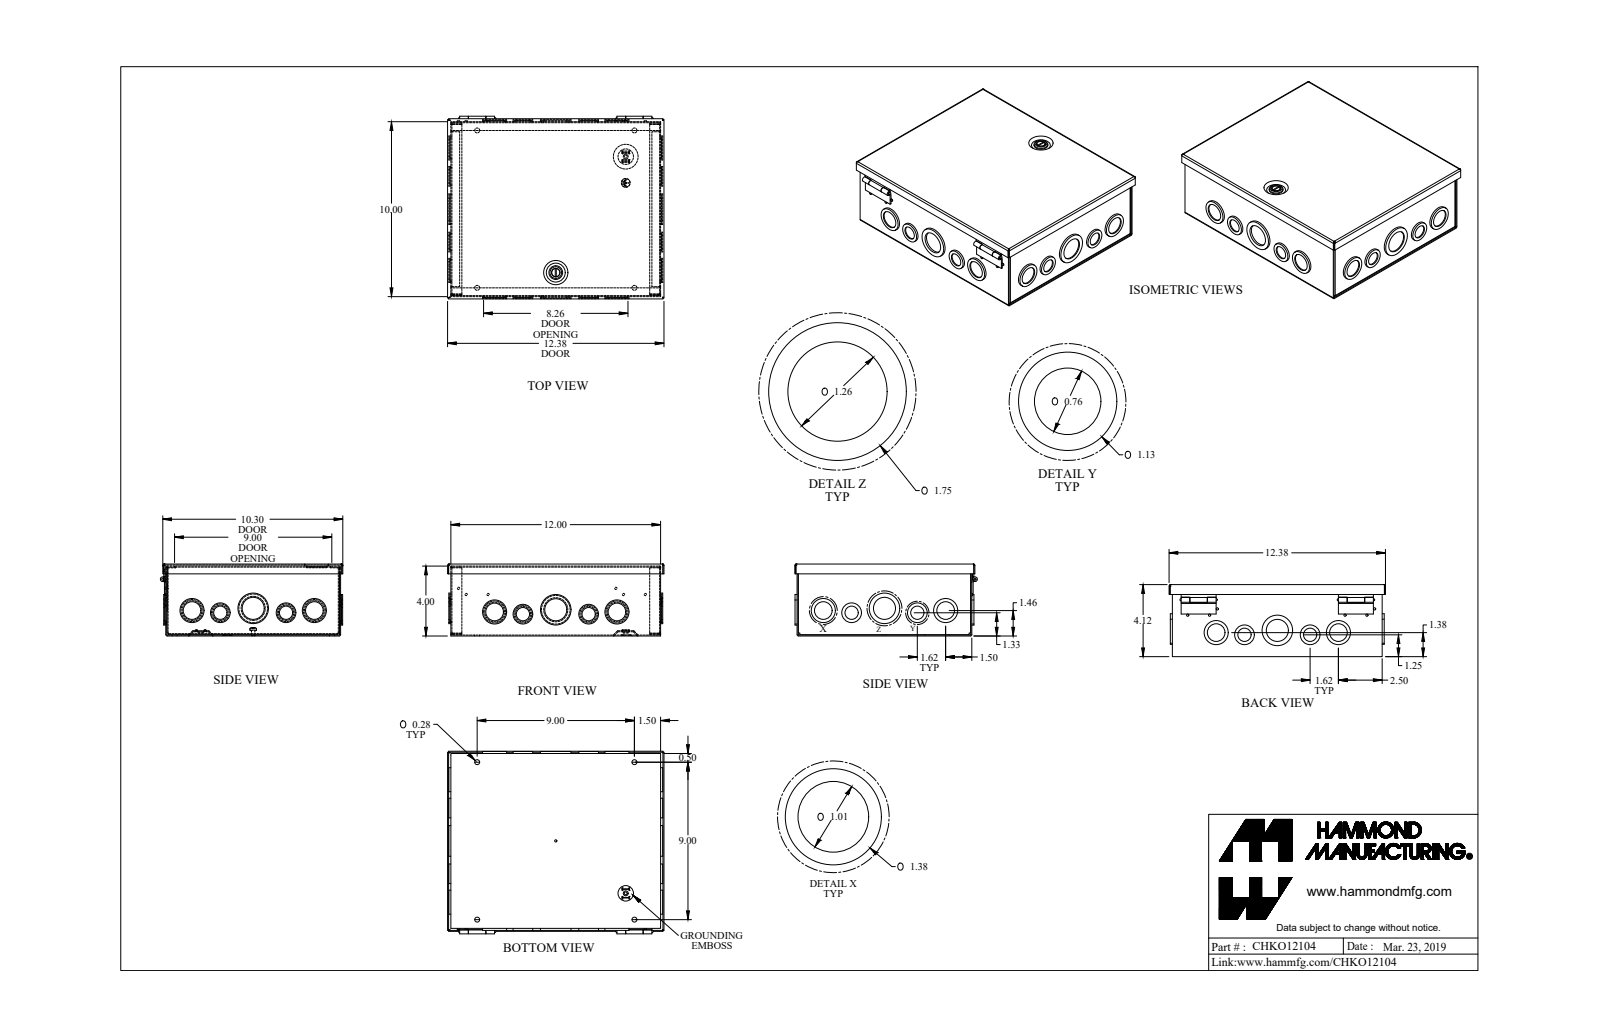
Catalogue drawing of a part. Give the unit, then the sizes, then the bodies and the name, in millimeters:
Units: millimetres
Overall size (bounding box): 314.5 × 265.3 × 104.6
Round holes (diameter × count): ⌀25.7 ×8, ⌀32 ×6, ⌀7.1 ×4, ⌀19.3 ×4, ⌀41.6 ×2, ⌀3.2 ×1, ⌀4.3 ×1, ⌀8.1 ×1, ⌀12.1 ×1, ⌀12.7 ×1
Round bosses / shafts (diameter × count): ⌀3.3 ×8, ⌀28.6 ×6, ⌀22.2 ×4, ⌀34.9 ×3, ⌀34.9 ×3, ⌀44.5 ×2, ⌀28.6 ×2, ⌀22.2 ×2
Partial cylindrical surfaces — rounded edges, fillets, slot ends (radius × count): R0.7 ×16, R2.2 ×16, R1.4 ×8, R0.3 ×4, R2.5 ×4, R0.9 ×2, R2 ×2, R6.4 ×2
Main face-to-face distances: 1.4, 103.1, 104.6, 101.7, 252.6, 303.4, 254, 304.8, 251.1, 100.2
Hole centre spacings: 41.3, 48.2, 89, 136.7, 228.6, 95.5, 177.8, 323.3
Volume: 473 900 mm³ · Surface area: 657 400 mm²
Bodies: 12 solids, 727 faces (352 planar, 332 cylindrical, 43 other)
Part name (STEP PRODUCT): CHKO12104_Default
STEP written by: SolidWorks 2019 (CONFIG_CONTROL_DESIGN)
